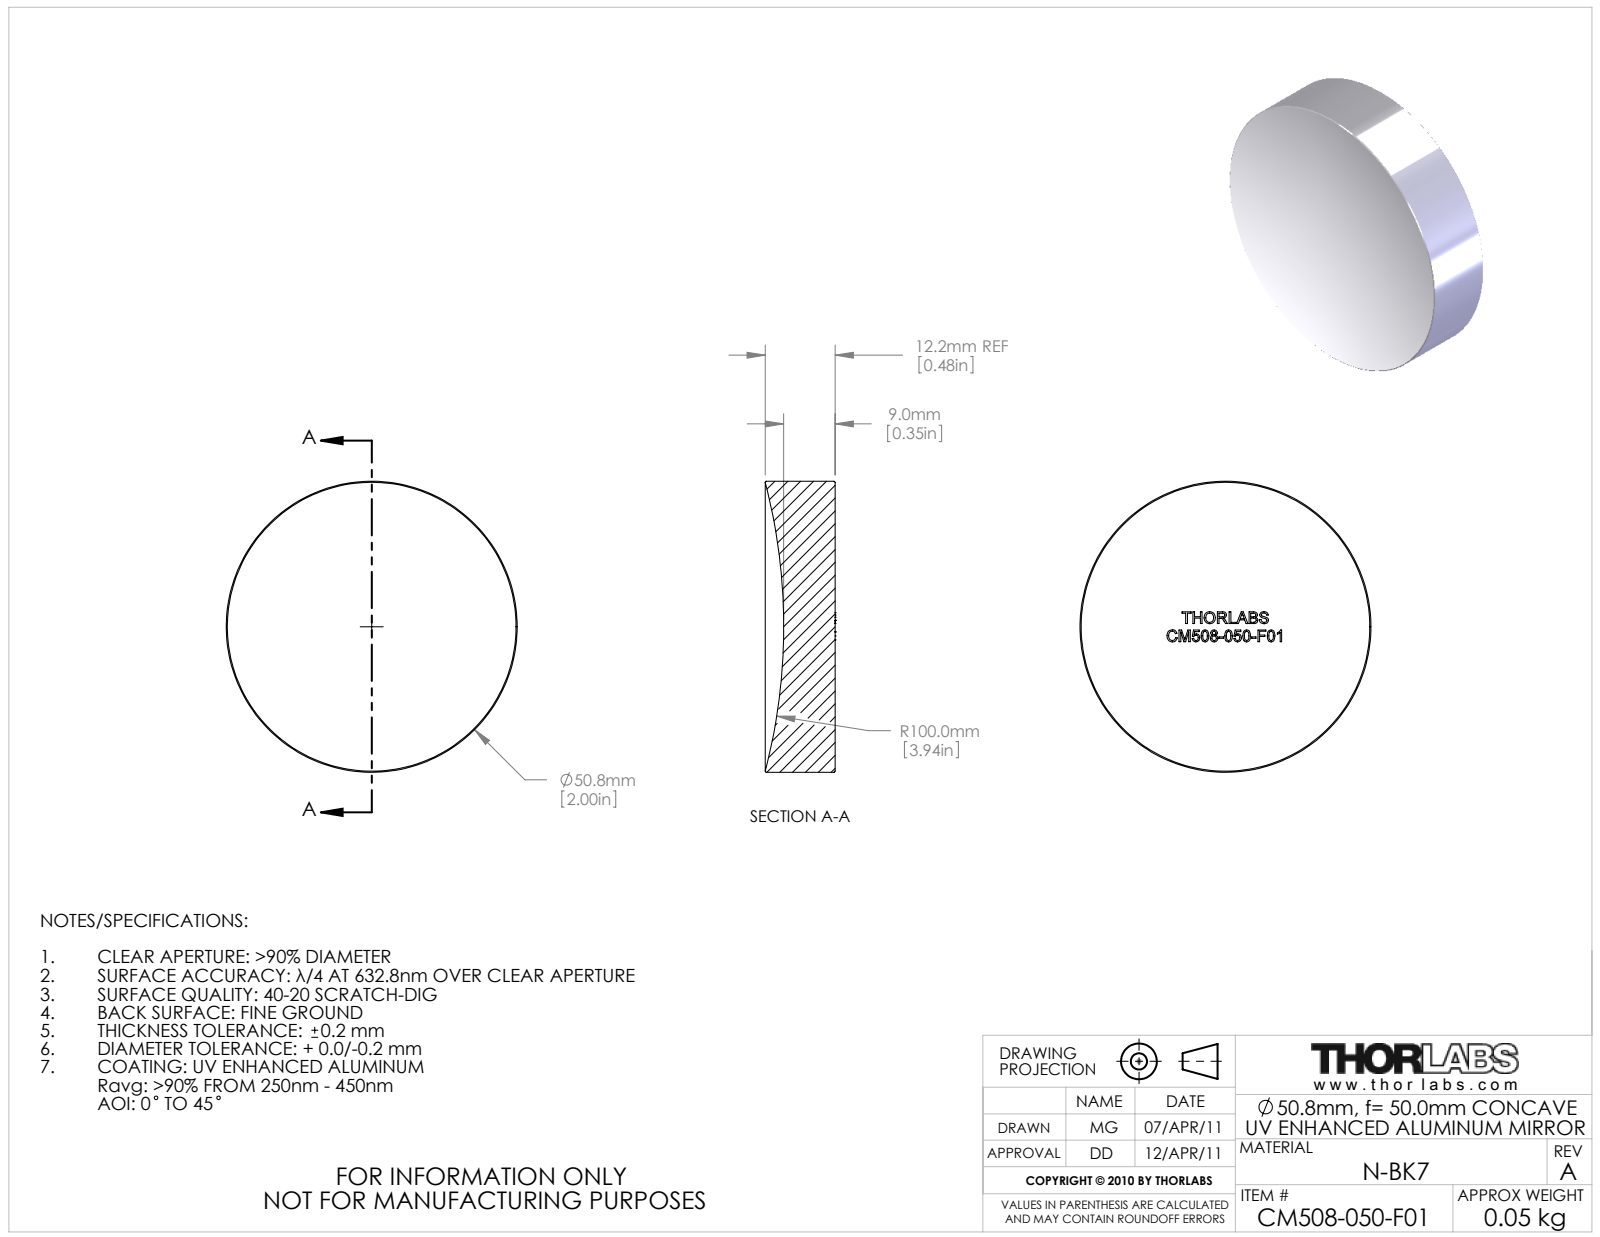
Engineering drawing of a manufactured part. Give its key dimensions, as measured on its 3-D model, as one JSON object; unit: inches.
{"part_name": "22198-E0W", "step_written_by": "SolidWorks 2011 (AUTOMOTIVE_DESIGN)", "units": "inches", "bodies": {"solids": 1, "faces": 280, "planar": 144, "cylindrical": 2, "other": 134}, "overall_size": [2, 2, 0.481], "volume_in3": 1.314, "surface_area_in2": 9.306, "round_bosses_or_shafts": [[2, 1]], "face_to_face_distances": [0.218, 0.046, 0.081, 0.124, 0.029, 0.1, 0.062, 0.081, 0.021, 0.249]}
